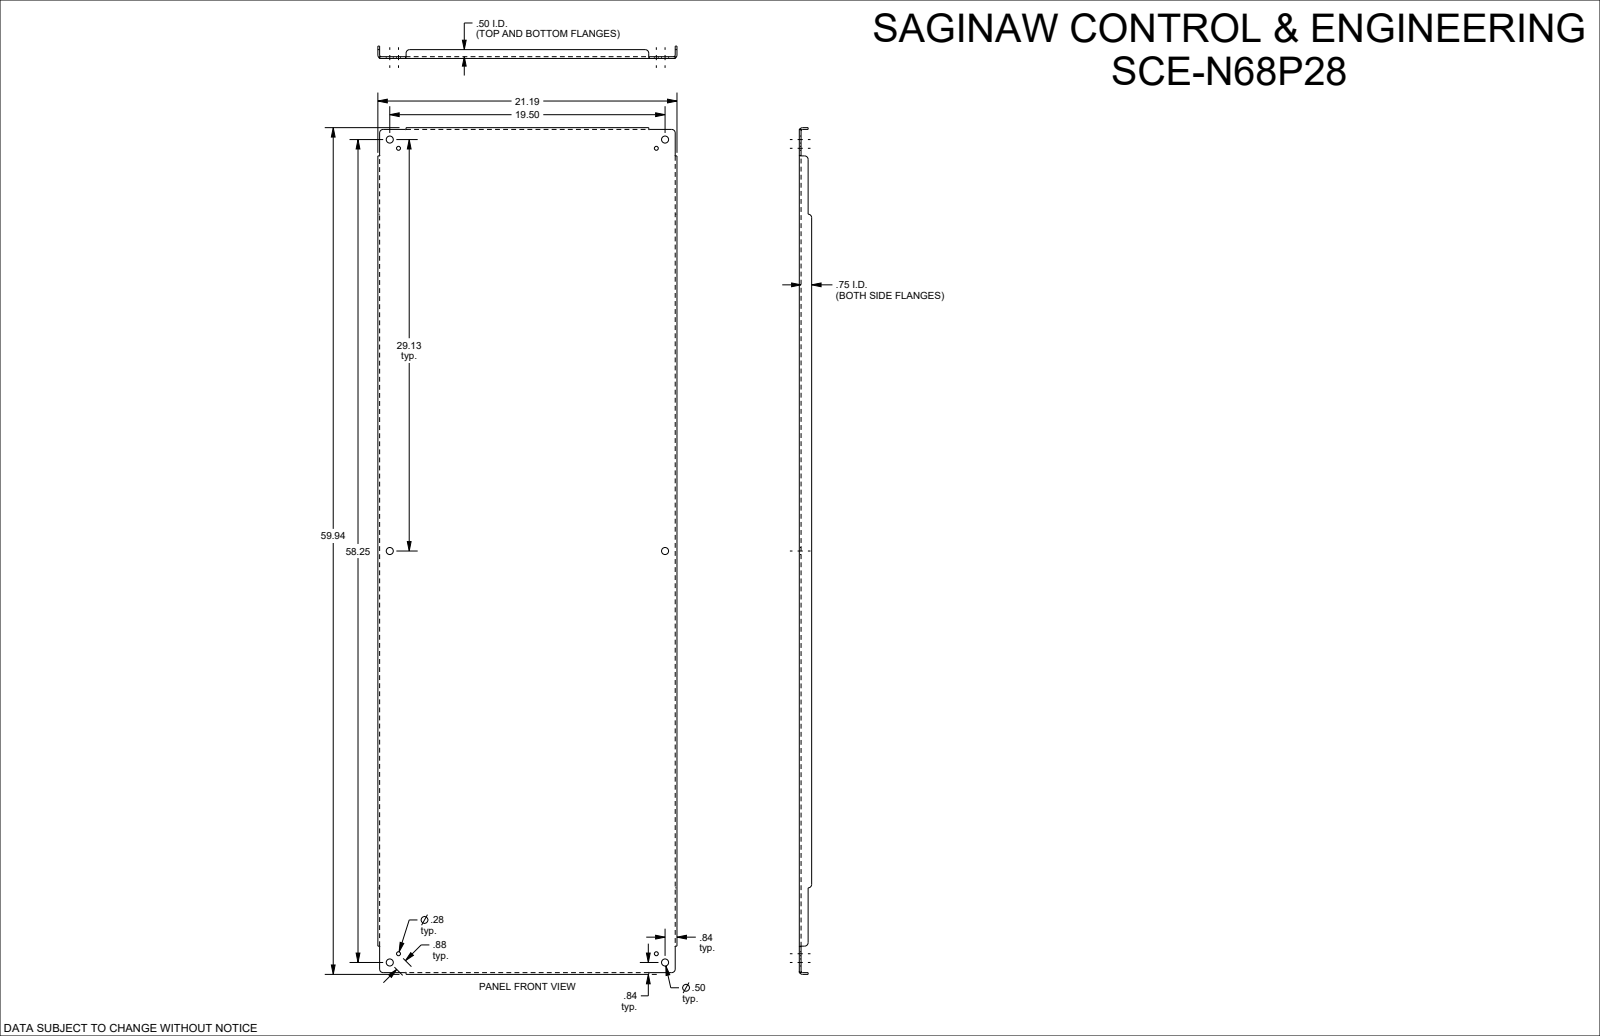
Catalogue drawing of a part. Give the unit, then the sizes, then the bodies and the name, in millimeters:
Units: millimetres
Overall size (bounding box): 1522.4 × 538.2 × 22.2
Round holes (diameter × count): ⌀12.7 ×6, ⌀7.1 ×4
Partial cylindrical surfaces — rounded edges, fillets, slot ends (radius × count): R6.4 ×11, R2.8 ×4, R6 ×4
Main face-to-face distances: 3.2, 535, 531.8, 538.1, 3.2, 1519.3, 19.1, 22.2, 1516, 1522.4
Hole centre spacings: 22.2, 479.8, 724.2, 739.8, 868.5, 890.3, 1463.9, 1540.4
Volume: 2 769 000 mm³ · Surface area: 1 759 000 mm²
Bodies: 1 solid, 110 faces (42 planar, 44 cylindrical, 24 other)
Part name (STEP PRODUCT): SCE-N68P28
STEP written by: SolidWorks 2023 (AUTOMOTIVE_DESIGN)
